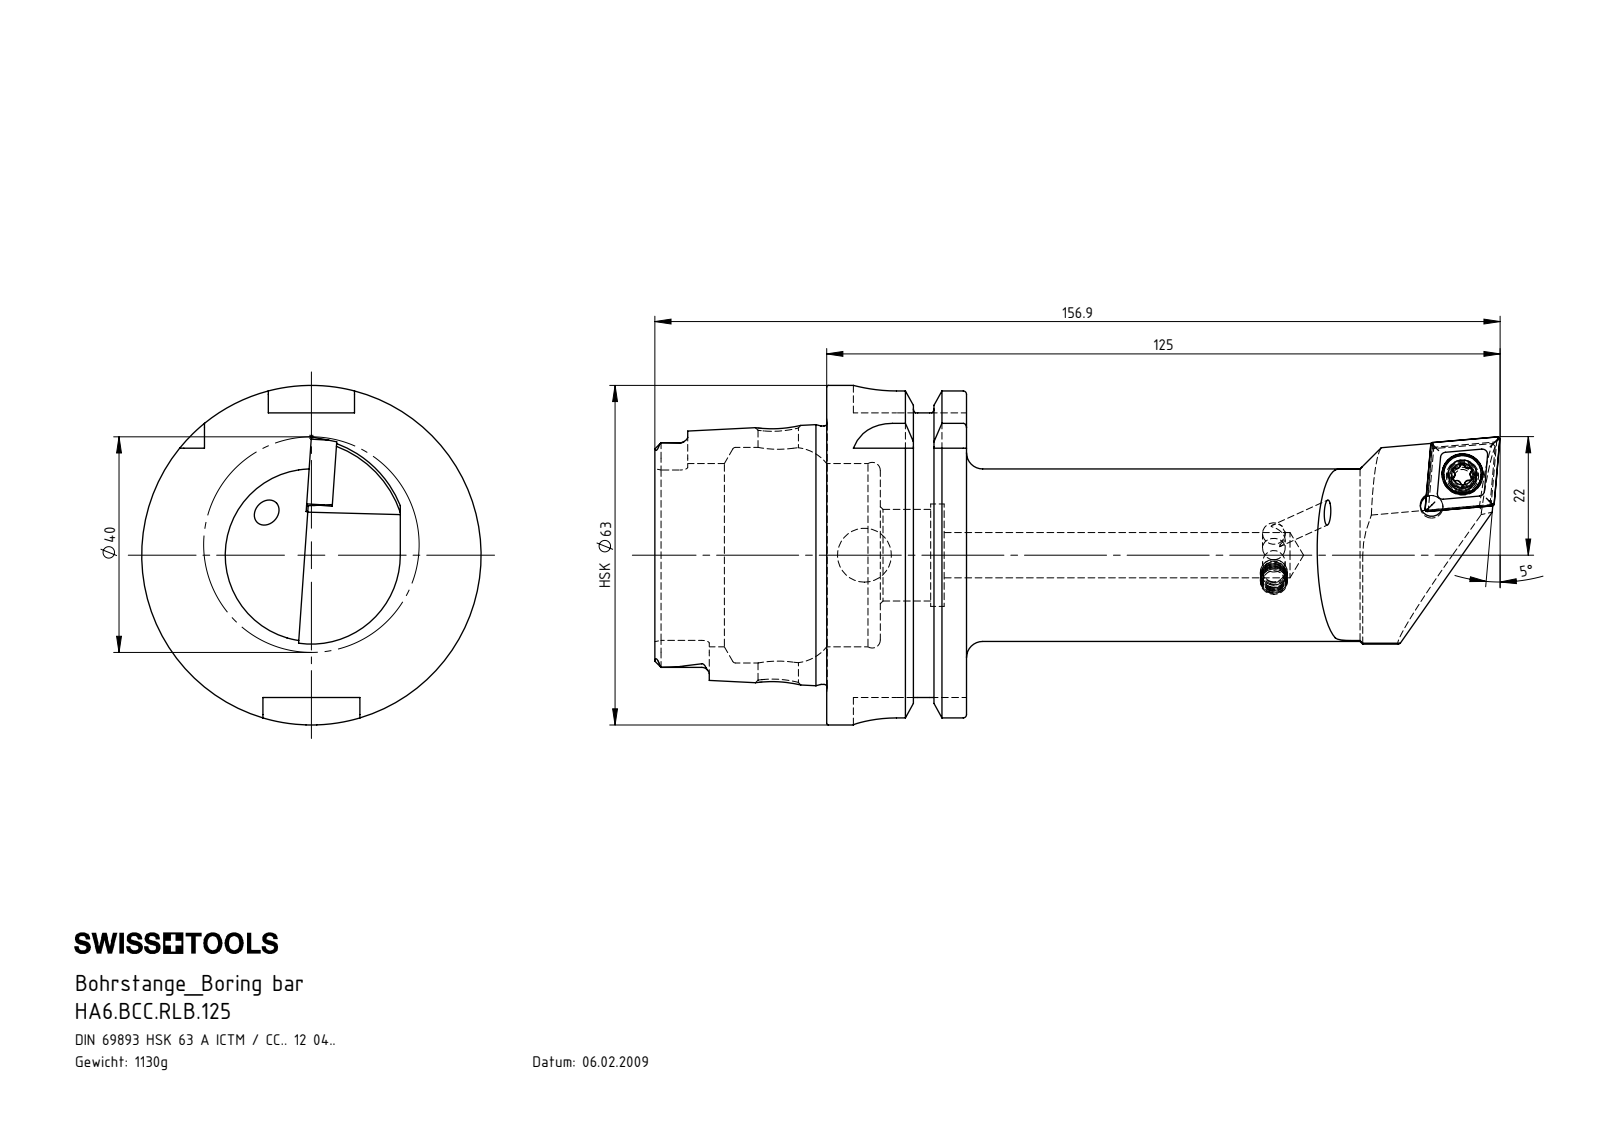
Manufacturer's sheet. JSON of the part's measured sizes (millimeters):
{"part_name": "KVT_MB_600_050; WCC-ER2.001.010_A; HA6-BCC.RLB.125_B; CCMT120404 (+1 more)", "step_written_by": "SolidWorks 2017 (AUTOMOTIVE_DESIGN)", "units": "millimeters", "bodies": {"solids": 5, "faces": 301, "planar": 75, "cylindrical": 90, "other": 136}, "overall_size": [156.86, 63, 63], "volume_mm3": 143981, "surface_area_mm2": 34318, "round_holes": [[4.2, 4], [4, 1], [5.5, 1], [7.5, 1], [7.6, 1], [8.4, 1], [10, 1], [17, 1], [19, 1], [34, 1], [40, 1]], "round_bosses_or_shafts": [[5, 2], [63, 1], [54.95, 1], [47.94, 1], [32, 1], [7, 1]], "partial_cylinders_radius": [[0.39, 6], [1.4, 6], [8, 4], [0.69, 3], [0.69, 3], [2.82, 2], [2.88, 2], [3, 1]], "face_to_face_distances": [25.95, 16, 9.95, 31.9, 41.85, 57.85, 52.8, 21.8, 11.85, 53.7], "hole_center_spacings": [8.09]}
